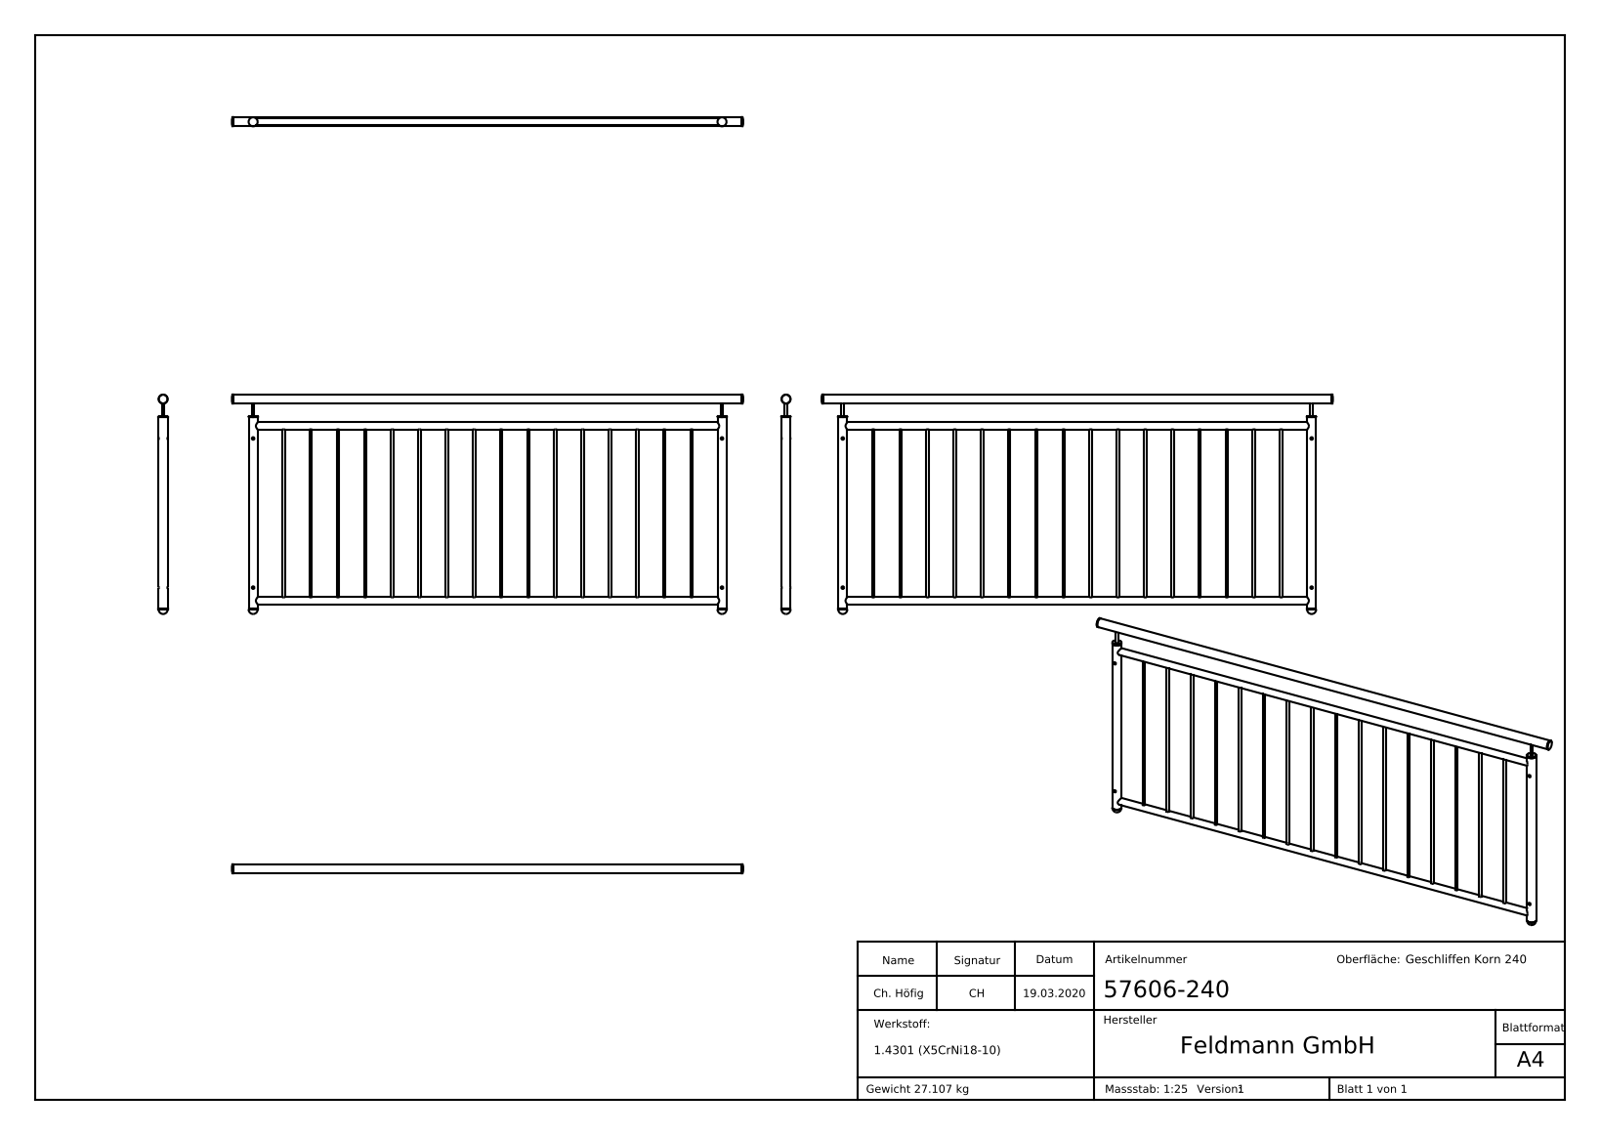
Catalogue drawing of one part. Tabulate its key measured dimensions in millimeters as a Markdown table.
| quantity | value |
| --- | --- |
| part name | 576XX-240 Teil2; Stopfen Konfig; 50236-240-60; 57606-240 (+7 more) |
| STEP written by | SolidWorks 2015 (CONFIG_CONTROL_DESIGN) |
| units | millimeters |
| bodies | 10 solids, 6682 faces (3197 planar, 1049 cylindrical, 2436 other) |
| overall size | 16102.4 × 8000 × 8000 |
| volume | 3 431 000 mm³ |
| surface area | 2 444 000 mm² |
| round holes (diameter × count) | 12 × 4, 38.4 × 3, 6.8 × 2, 29.7 × 2, 34.5 × 2, 34.6 × 1 |
| round bosses / shafts (diameter × count) | 12 × 18, 42.4 × 3, 37.5 × 3, 33.7 × 2, 8 × 2, 6 × 2 |
| partial cylindrical surfaces (radius × count) | 2 × 4, 19.4 × 3, 17.35 × 2, 19.3 × 1 |
| main face-to-face distances | 13, 5, 8, 890.6, 898.6, 903.6, 18.7, 18.75, 2386, 18.76 |
| hole center spacings | 2200, 700, 2308.68, 126.2, 820, 946.2 |
